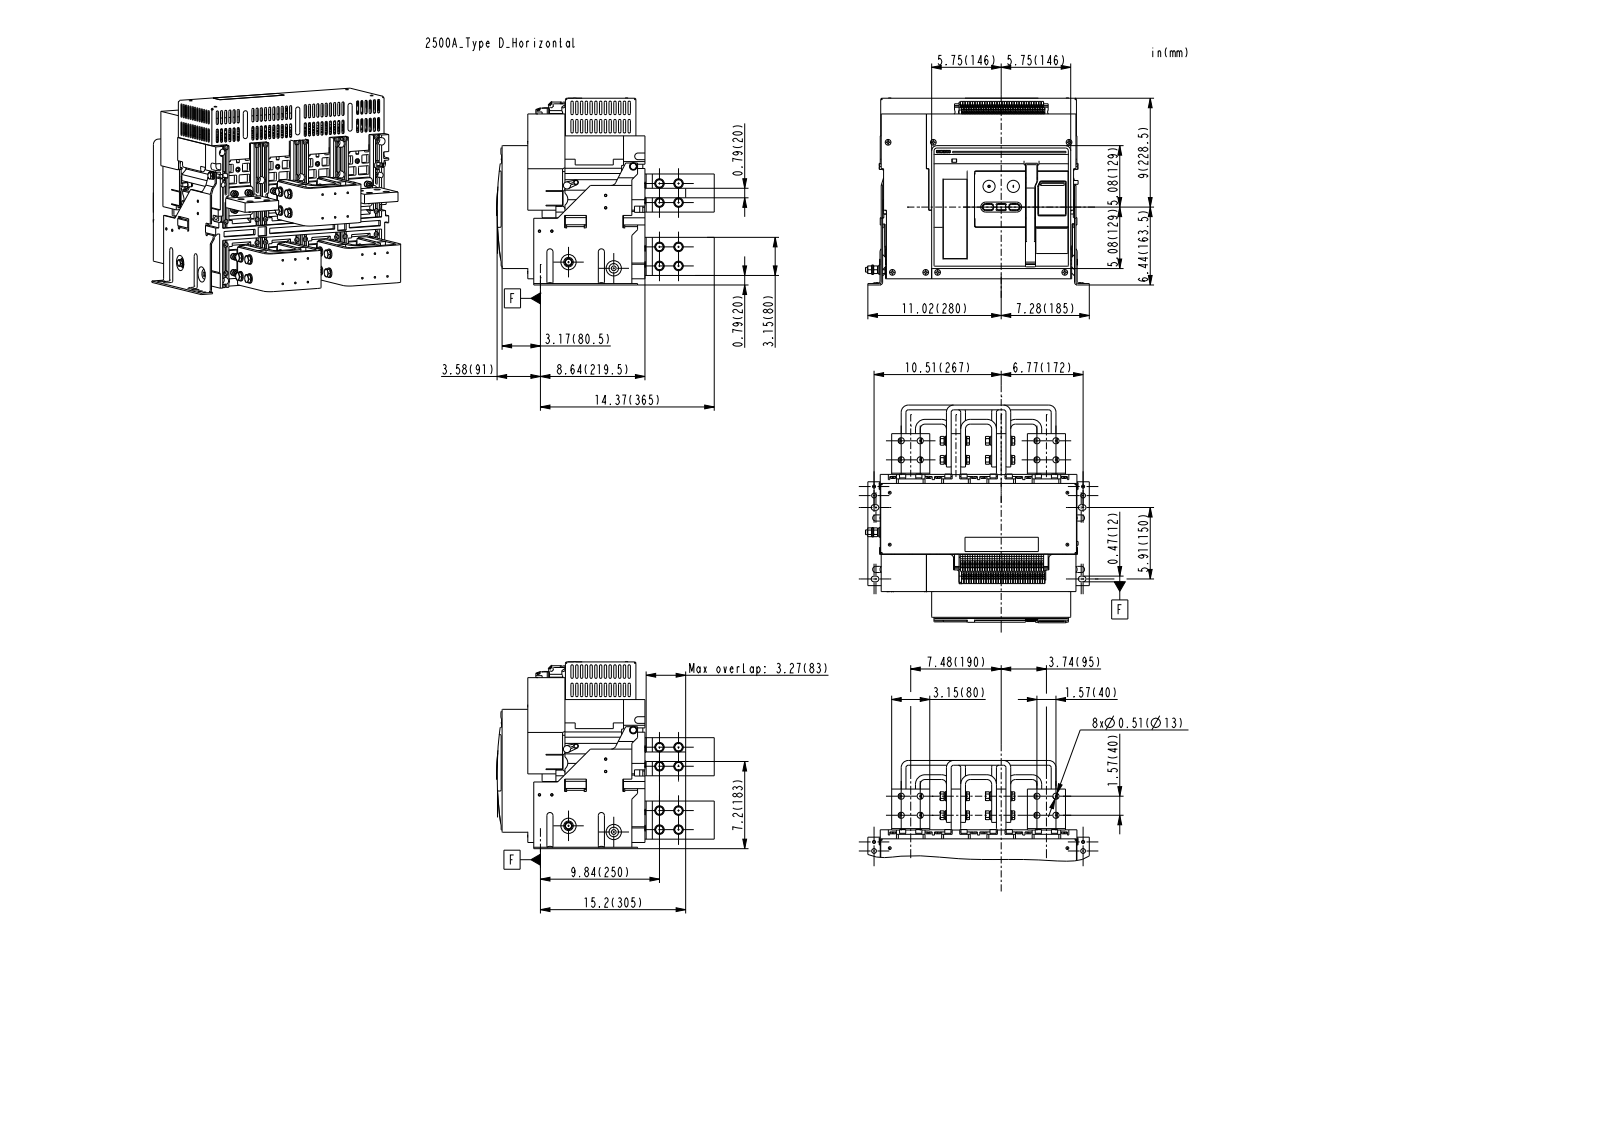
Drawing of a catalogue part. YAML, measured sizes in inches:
part_name: "2500A_TYPE_D_HORIZONTAL"
step_written_by: "CREO PARAMETRIC BY PTC INC, 2020044 (CONFIG_CONTROL_DESIGN)"
units: inches
bodies: {solids: 17, faces: 15320, planar: 9197, cylindrical: 4259, other: 1864}
overall_size: [18.504, 17.989, 15.469]
volume: 668.2
surface_area: 5673
round_holes:
  - {diameter: 0.157, count: 104}
  - {diameter: 0.335, count: 43}
  - {diameter: 0.319, count: 39}
  - {diameter: 0.118, count: 30}
  - {diameter: 0.394, count: 29}
  - {diameter: 0.256, count: 25}
  - {diameter: 0.194, count: 23}
  - {diameter: 0.472, count: 16}
  - {diameter: 0.512, count: 16}
  - {diameter: 0.61, count: 11}
  - {diameter: 0.244, count: 10}
  - {diameter: 0.354, count: 9}
round_bosses_or_shafts:
  - {diameter: 0.315, count: 47}
  - {diameter: 0.484, count: 34}
  - {diameter: 0.262, count: 34}
  - {diameter: 0.512, count: 32}
  - {diameter: 0.236, count: 26}
  - {diameter: 0.157, count: 24}
  - {diameter: 0.354, count: 22}
  - {diameter: 0.13, count: 18}
partial_cylinders:
  - {radius: 0.079, count: 269}
  - {radius: 0.098, count: 187}
  - {radius: 0.039, count: 157}
  - {radius: 0.118, count: 66}
  - {radius: 0.02, count: 41}
  - {radius: 0.059, count: 35}
  - {radius: 0.207, count: 32}
  - {radius: 0.008, count: 24}
face_to_face_distances: [0.157, 3.74, 0.059, 14.862, 0.118, 7.48, 0.315, 0.039, 5.807, 6.142]
hole_center_spacings: [1.575, 3.74, 2.227, 0.591, 4.878, 6.119, 4.331, 4.843]
